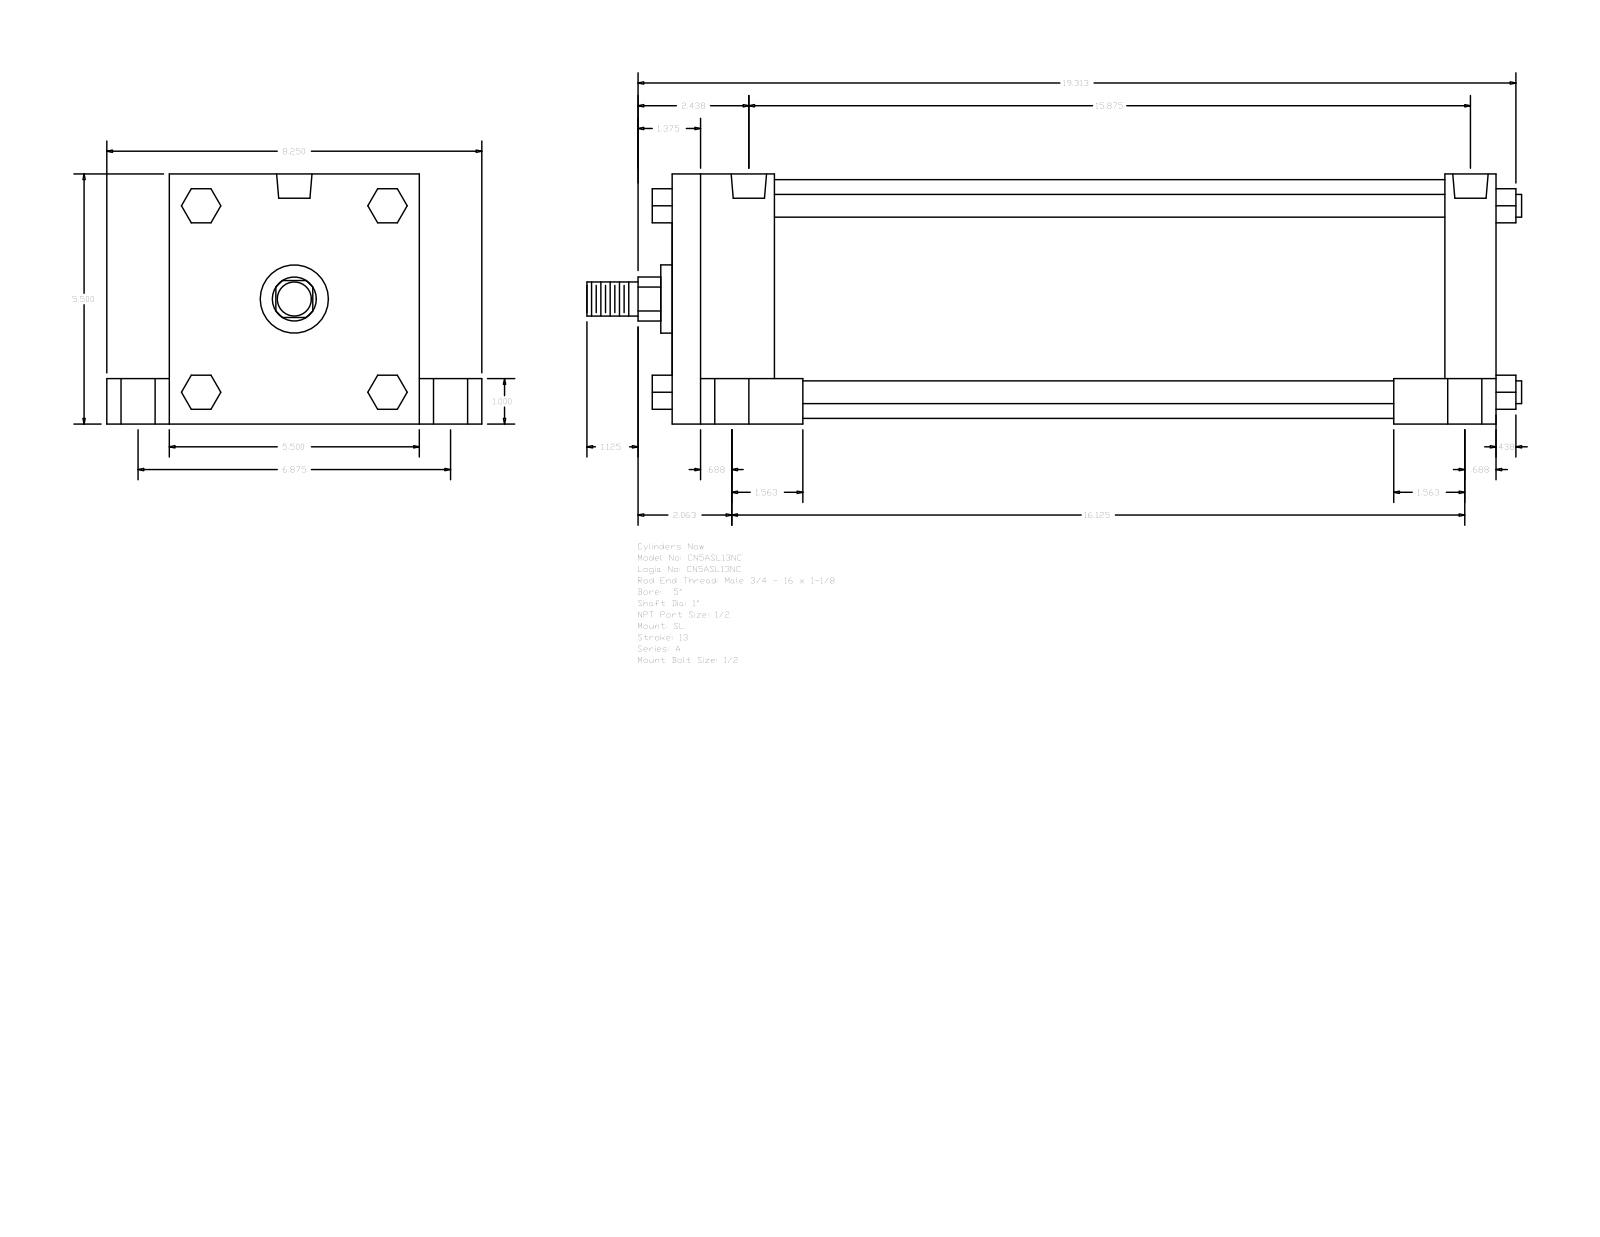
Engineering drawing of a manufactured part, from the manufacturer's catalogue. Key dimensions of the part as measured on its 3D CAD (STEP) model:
Part name (STEP PRODUCT): A_SL__0500_1
STEP written by: GSSL Pune (CONFIG_CONTROL_DESIGN)
Units: millimetres
Bodies: 0 solids, 150 faces (114 planar, 36 cylindrical, 0 other)
Overall size (bounding box): 522.29 × 209.55 × 139.7
Round holes (diameter × count): ⌀8.73 ×4, ⌀19.05 ×4, ⌀25.4 ×4, ⌀19.77 ×2
Round bosses / shafts (diameter × count): ⌀12.7 ×4, ⌀133.35 ×1, ⌀38.1 ×1, ⌀25.4 ×1, ⌀19.05 ×1
Partial cylindrical surfaces — rounded edges, fillets, slot ends (radius × count): R12.29 ×1
Main face-to-face distances: 139.7, 460.38, 28.58, 25.4, 114.3, 34.93, 174.63, 57.15, 431.8, 374.65
Hole centre spacings: 2.39, 87.31, 87.37, 87.83, 88.12, 174.62, 398.45, 400.84
